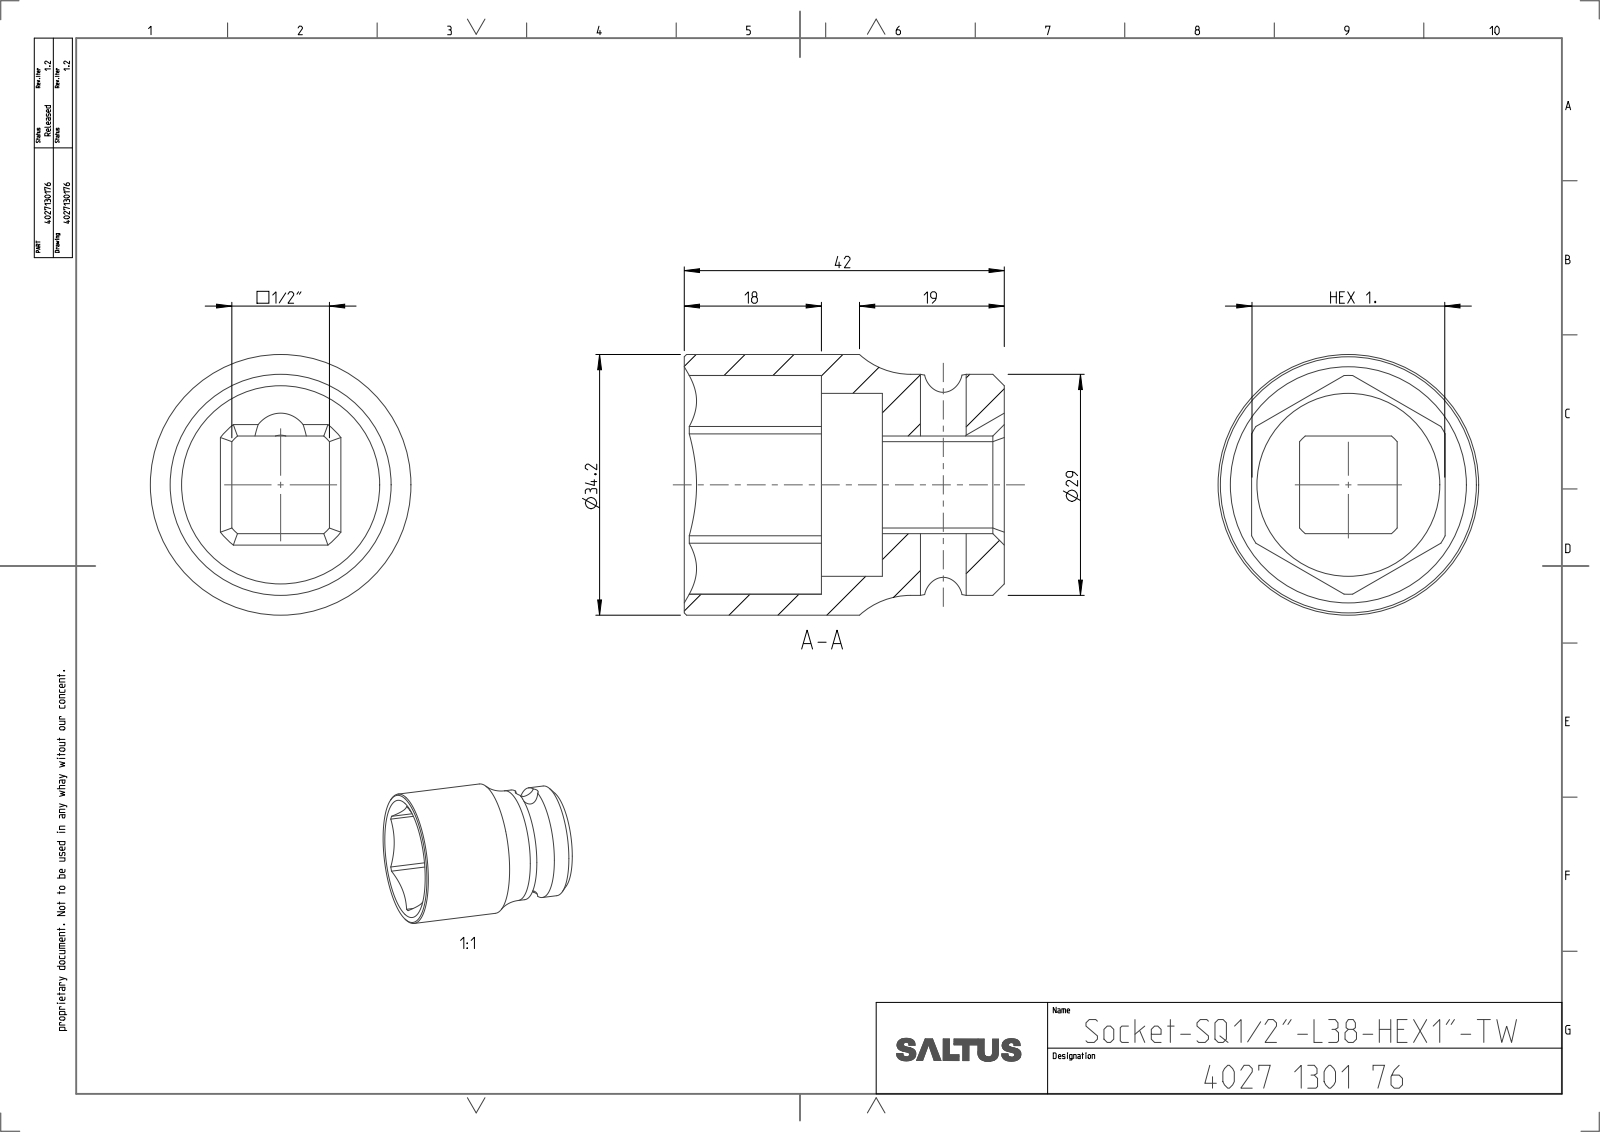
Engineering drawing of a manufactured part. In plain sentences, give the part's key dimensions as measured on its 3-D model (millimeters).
The part is named "4027130176". Its 3-D file was written by "CREO PARAMETRIC BY PTC INC, 2022414 (CONFIG_CONTROL_DESIGN)". It is 1 solid with 55 faces: 18 planar, 21 cylindrical and 16 other. Overall it measures 43 by 43 by 42 millimeters. Its volume is 24 224 cubic millimeters and its surface area 10 334 square millimeters. Round holes: 1 of diameter 6, 1 of diameter 24. Round bosses or shafts: 1 of diameter 43, 1 of diameter 29. Partial cylindrical surfaces (rounded edges, fillets, slot ends): 1 of radius 4, 1 of radius 8.55, 1 of radius 18.08. The main face-to-face distances are 32, 9.59, 22.41, 24, 12.82, 42, 18.
